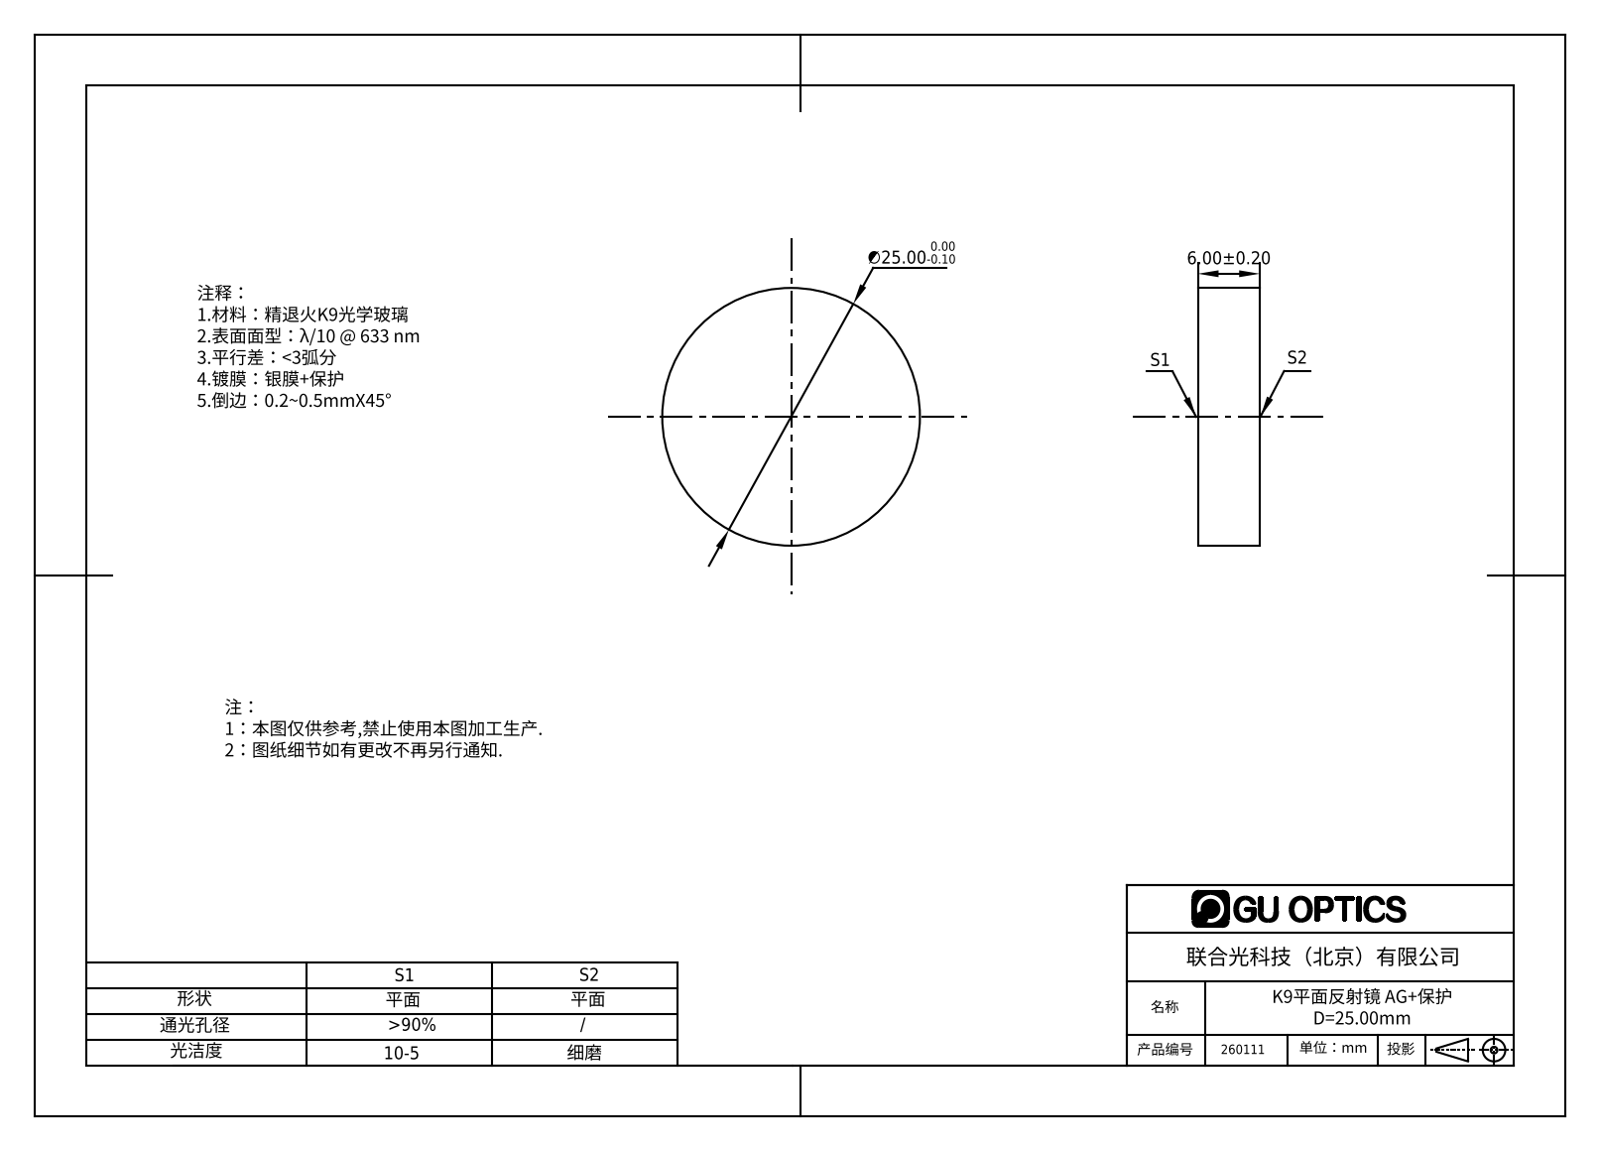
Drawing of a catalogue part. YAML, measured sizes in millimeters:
part_name: "260072"
step_written_by: "SolidWorks 2016 (AUTOMOTIVE_DESIGN)"
units: millimeters
bodies: {solids: 1, faces: 4, planar: 2, cylindrical: 2, other: 0}
overall_size: [25, 25, 6]
volume: 2945
surface_area: 1453
round_bosses_or_shafts:
  - {diameter: 25, count: 1}
face_to_face_distances: [6]
